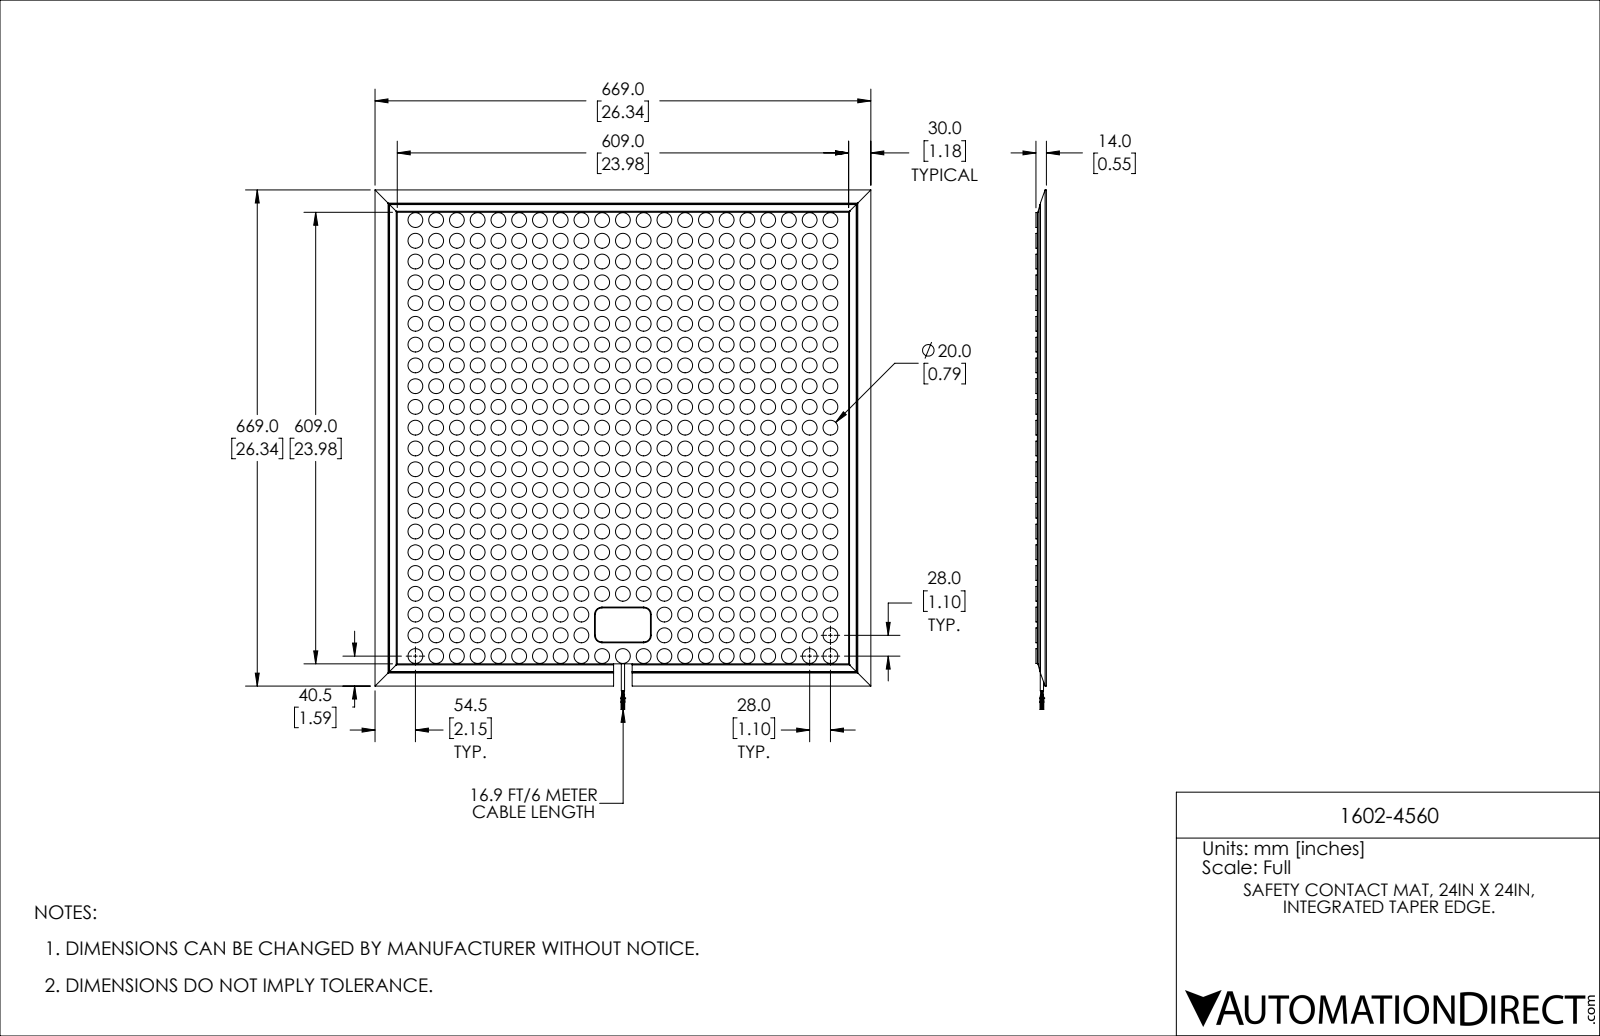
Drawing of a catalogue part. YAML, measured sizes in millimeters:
part_name: "1602-4560"
step_written_by: "SolidWorks 2021 (AUTOMOTIVE_DESIGN)"
units: millimeters
bodies: {solids: 461, faces: 2025, planar: 990, cylindrical: 994, other: 41}
overall_size: [700.5, 669, 14]
volume: 5175000
surface_area: 1321000
round_bosses_or_shafts:
  - {diameter: 20, count: 456}
  - {diameter: 1.2, count: 20}
  - {diameter: 0.8, count: 8}
  - {diameter: 4.4, count: 1}
partial_cylinders:
  - {radius: 1, count: 4}
  - {radius: 10, count: 4}
face_to_face_distances: [12, 2, 14, 609, 3.5, 1.5, 10.5, 3.4, 1.4, 10.6]
